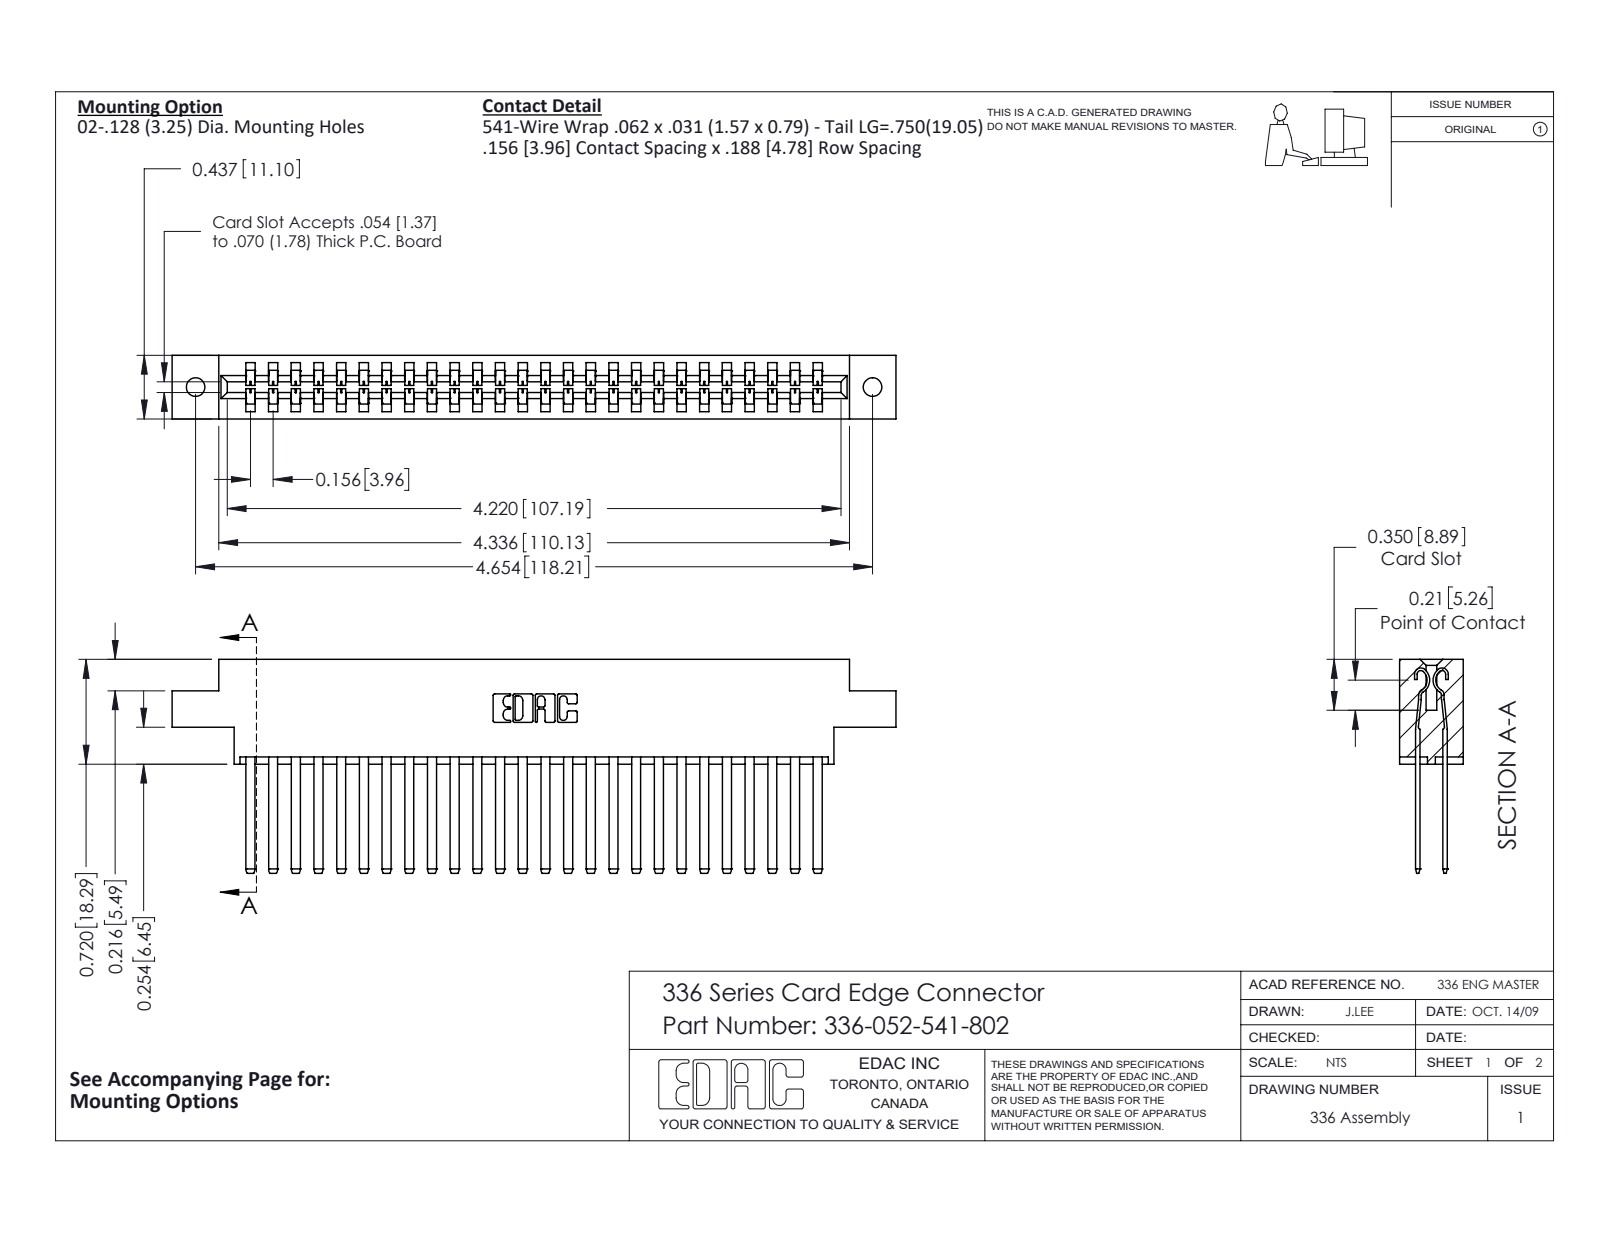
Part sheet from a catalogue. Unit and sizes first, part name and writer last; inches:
Units: inches
Overall size (bounding box): 4.977 × 1.47 × 0.437
Round holes (diameter × count): ⌀0.128 ×2
Partial cylindrical surfaces — rounded edges, fillets, slot ends (radius × count): R0.004 ×104, R0.056 ×52, R0.01 ×22, R0.007 ×6, R0.031 ×6, R0.022 ×4, R0.04 ×4, R0.026 ×3
Main face-to-face distances: 0.188, 0.328, 0.14, 0.297, 0.109, 0.031, 0.437, 0.033, 0.181, 0.256
Hole centre spacings: 4.654
Volume: 1.149 in³ · Surface area: 36.76 in²
Bodies: 53 solids, 2302 faces (1426 planar, 876 cylindrical, 0 other)
Part name (STEP PRODUCT): 336-290-001_336-290-541; 336-052-541-802; 336 Part_Offset - .128 Dia
STEP written by: SolidWorks 2020 (CONFIG_CONTROL_DESIGN)
